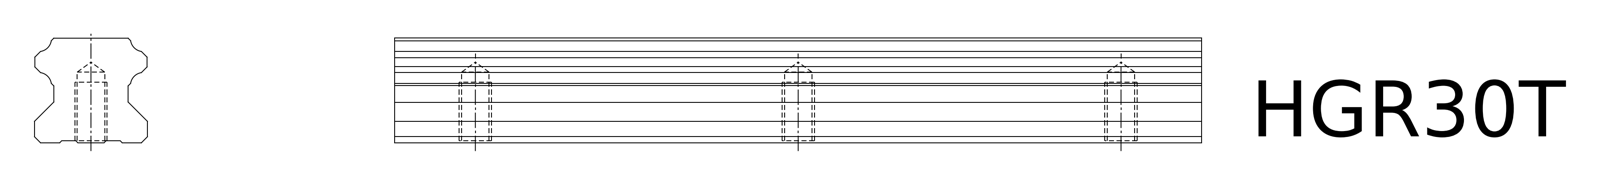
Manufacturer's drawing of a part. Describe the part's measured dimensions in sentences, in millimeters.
The part is named "HGR30T". Its 3-D file was written by "SolidWorks 2006104 (CONFIG_CONTROL_DESIGN)". It is 1 solid with 61 faces: 33 planar, 28 cylindrical and 0 other. Overall it measures 200 by 28 by 26 millimeters. Its volume is 120 389 cubic millimeters and its surface area 24 412 square millimeters. Round holes: 3 of diameter 8. Partial cylindrical surfaces (rounded edges, fillets, slot ends): 12 of radius 0.6, 6 of radius 0.8, 4 of radius 2.83. The main face-to-face distances are 26, 4.7, 23.3, 28, 11.18, 33.76, 22.58, 21.57, 10.39, 12.19. The hole center spacings are 80, 160.
